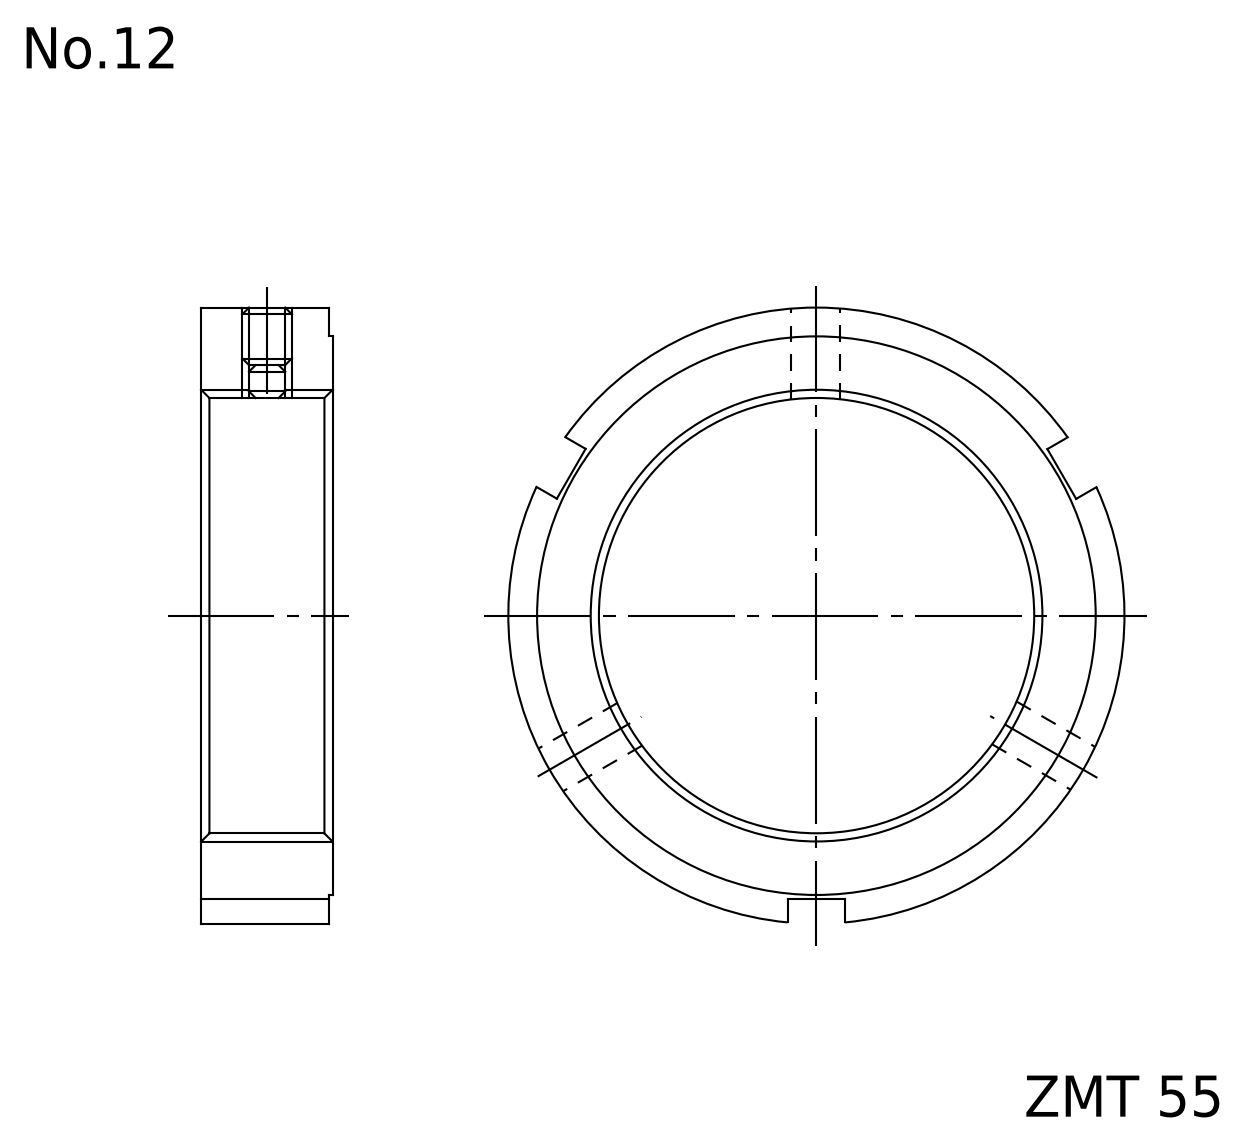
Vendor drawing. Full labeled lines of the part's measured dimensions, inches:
Part name (STEP PRODUCT): FKD ZMT 55
STEP written by: Autodesk Inventor 2011 (AUTOMOTIVE_DESIGN)
Units: inches
Bodies: 1 solid, 20 faces (12 planar, 8 cylindrical, 0 other)
Overall size (bounding box): 2.953 × 2.946 × 0.63
Volume: 1.877 in³ · Surface area: 17.2 in²
Round holes (diameter × count): ⌀0.194 ×3, ⌀2.165 ×1
Round bosses / shafts (diameter × count): ⌀2.953 ×1, ⌀2.677 ×1
Main face-to-face distances: 0.63, 0.02, 0.61, 0.276
